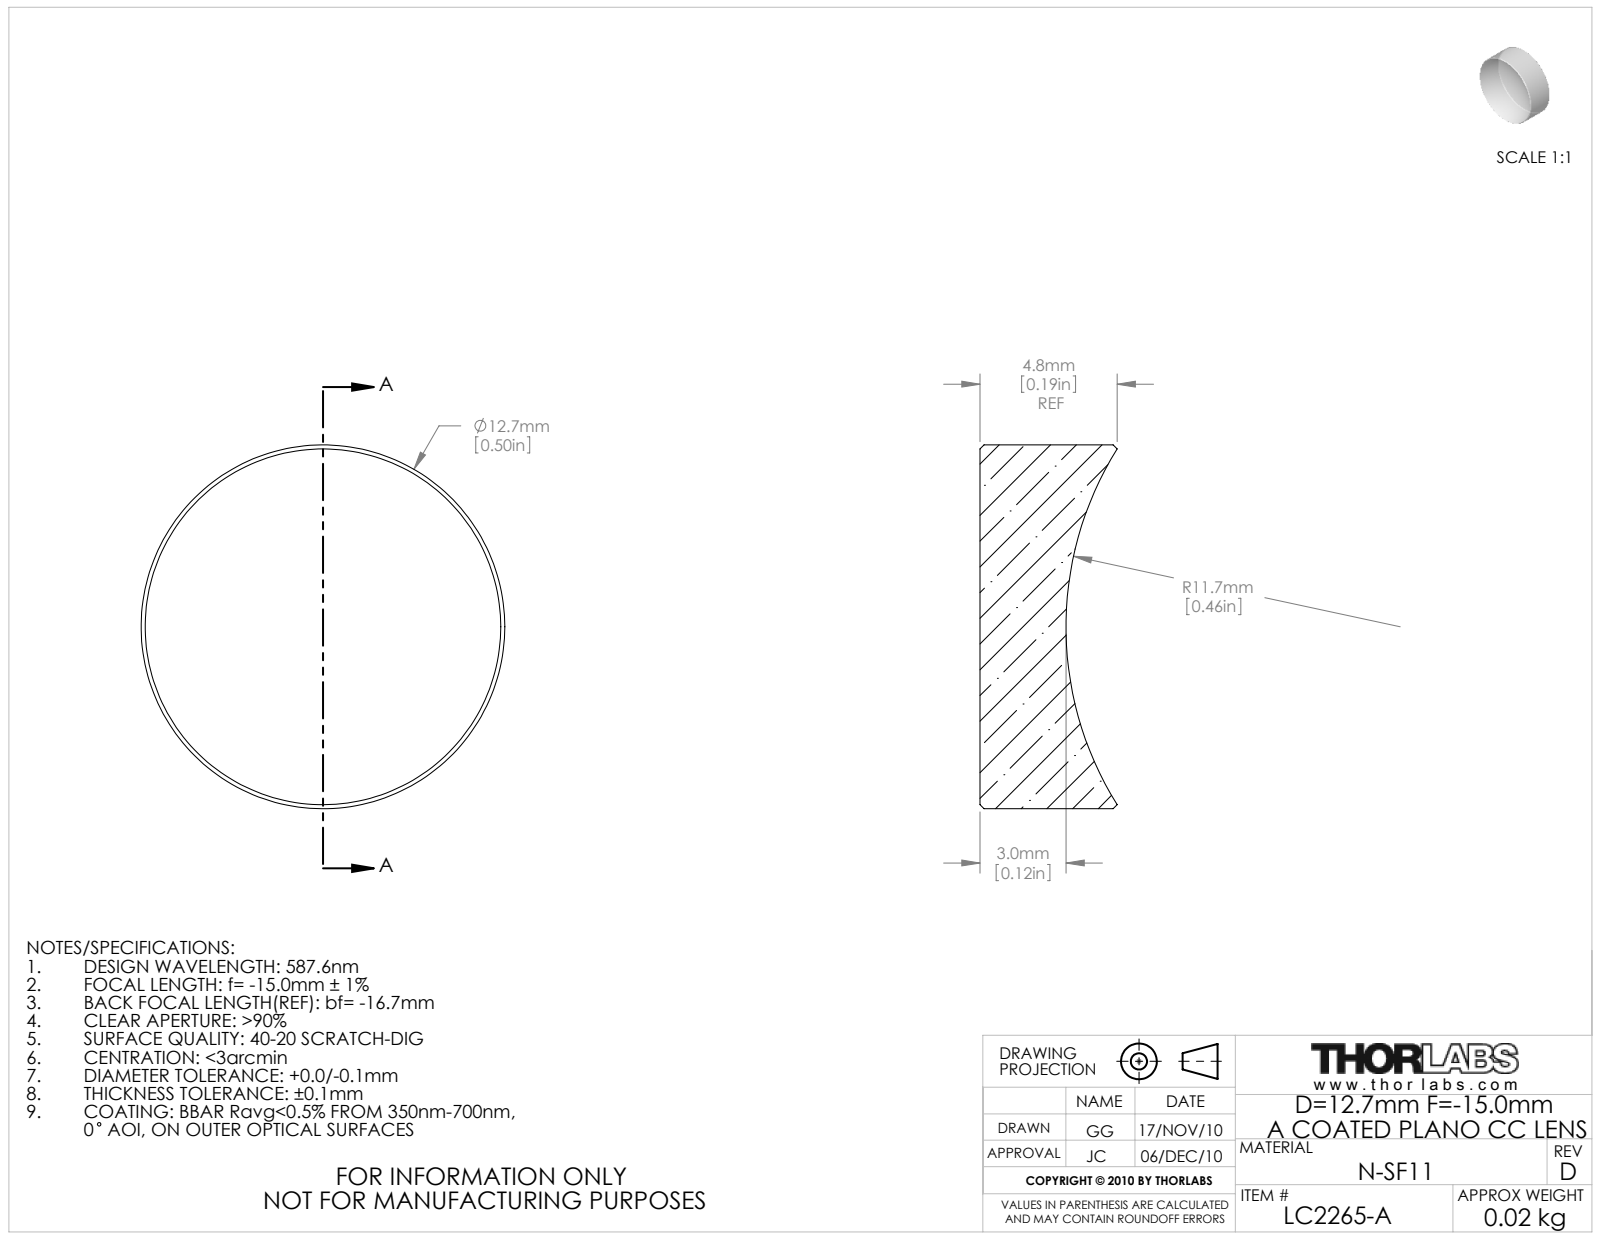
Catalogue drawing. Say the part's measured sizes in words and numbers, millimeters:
The part is named "5436-E0W". Its 3-D file was written by "SolidWorks 2009 (AUTOMOTIVE_DESIGN)". It is 1 solid with 9 faces: 1 planar, 2 cylindrical and 6 other. Overall it measures 12.7 by 12.7 by 4.79 millimeters. Its volume is 495 cubic millimeters and its surface area 448 square millimeters. Round bosses or shafts: 1 of diameter 12.7.
